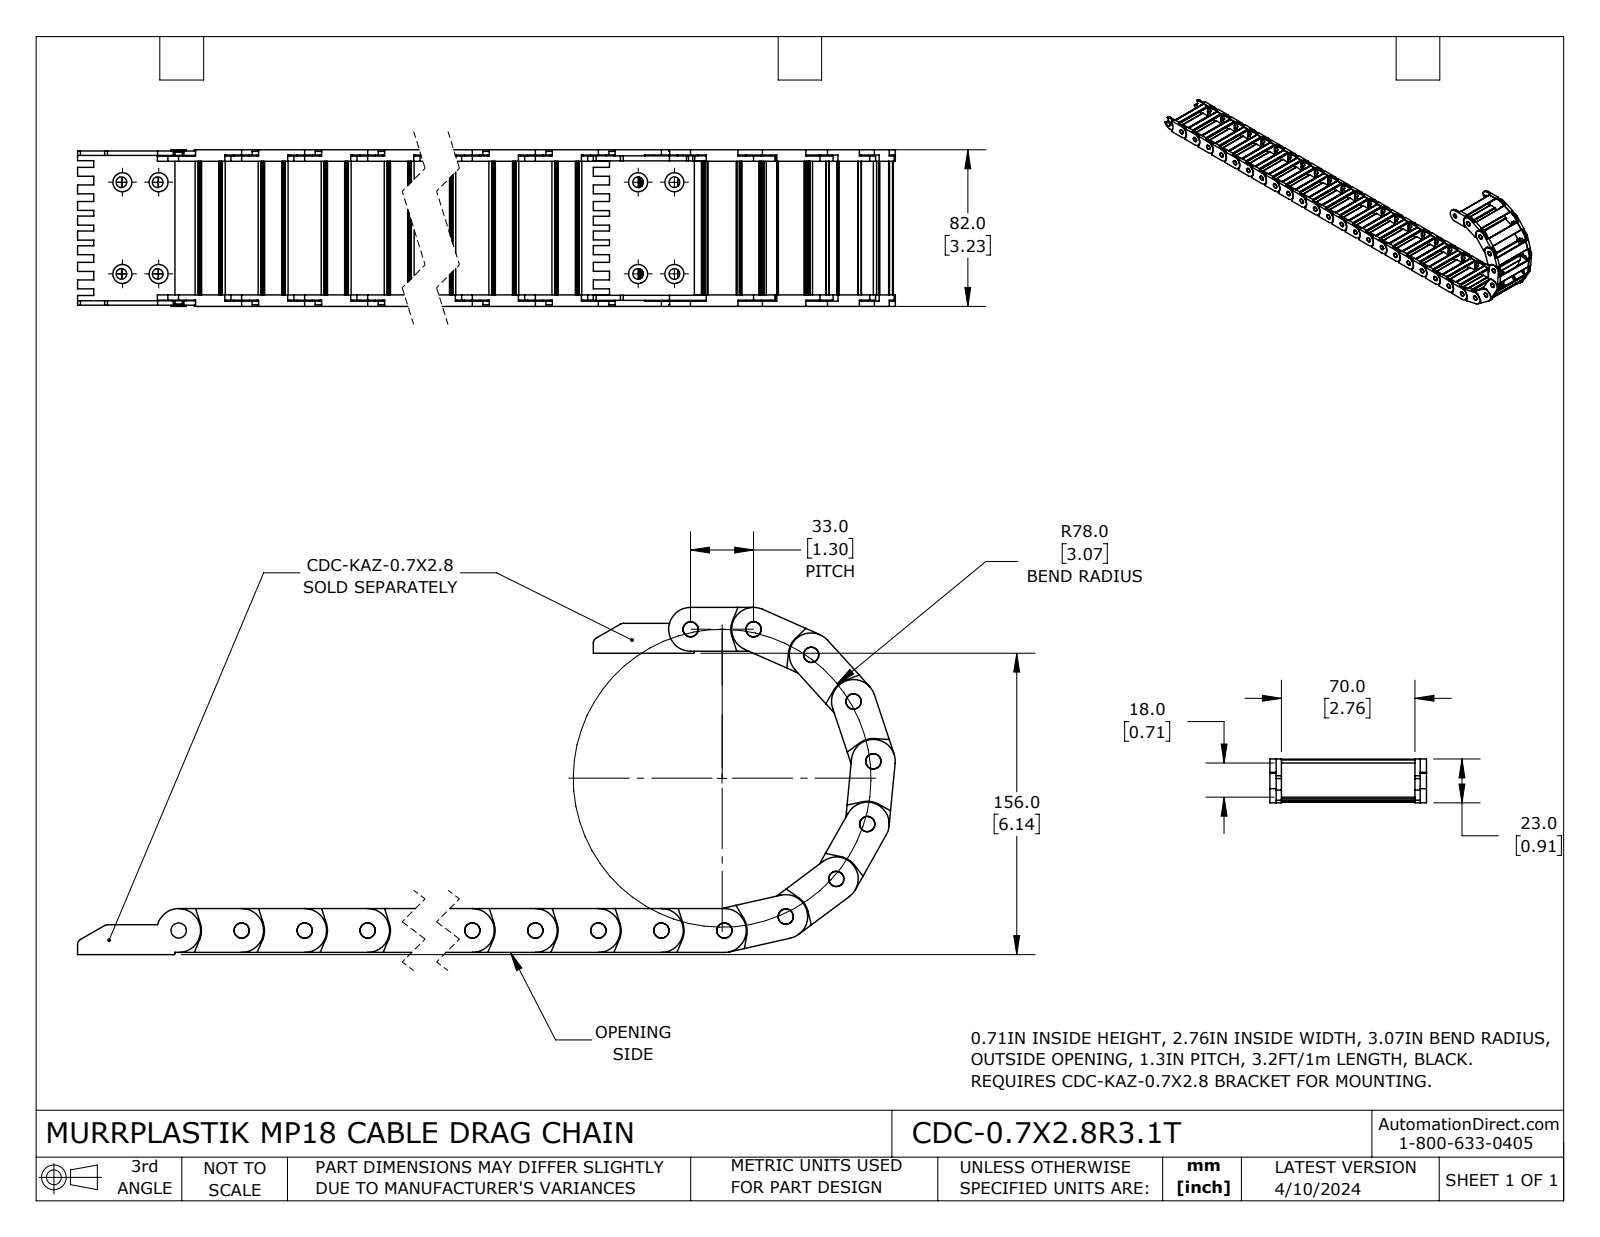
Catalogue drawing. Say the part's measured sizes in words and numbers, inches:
The part is named "CDC-0.7X2.8R3.1T". Its 3-D file was written by "SolidWorks 2023 (CONFIG_CONTROL_DESIGN)". It is 30 solids with 2280 faces: 1110 planar, 1170 cylindrical and 0 other. Overall it measures 32.549 by 7.115 by 3.228 inches. Its volume is 21.04 cubic inches and its surface area 462.3 square inches. Round holes: 30 of diameter 0.315. Round bosses or shafts: 1 of diameter 0.315. Partial cylindrical surfaces (rounded edges, fillets, slot ends): 120 of radius 0.02, 120 of radius 0.059, 60 of radius 0.008, 60 of radius 0.012, 31 of radius 0.453, 31 of radius 0.47, 30 of radius 0.197, 30 of radius 0.215. The main face-to-face distances are 2.992, 0.106, 0.13, 0.236, 0.079, 3.228, 3.098, 2.862, 3.122, 0.024. The hole center spacings are 1.299, 2.598, 3.898, 5.197, 6.496, 7.795, 9.094, 10.394.
